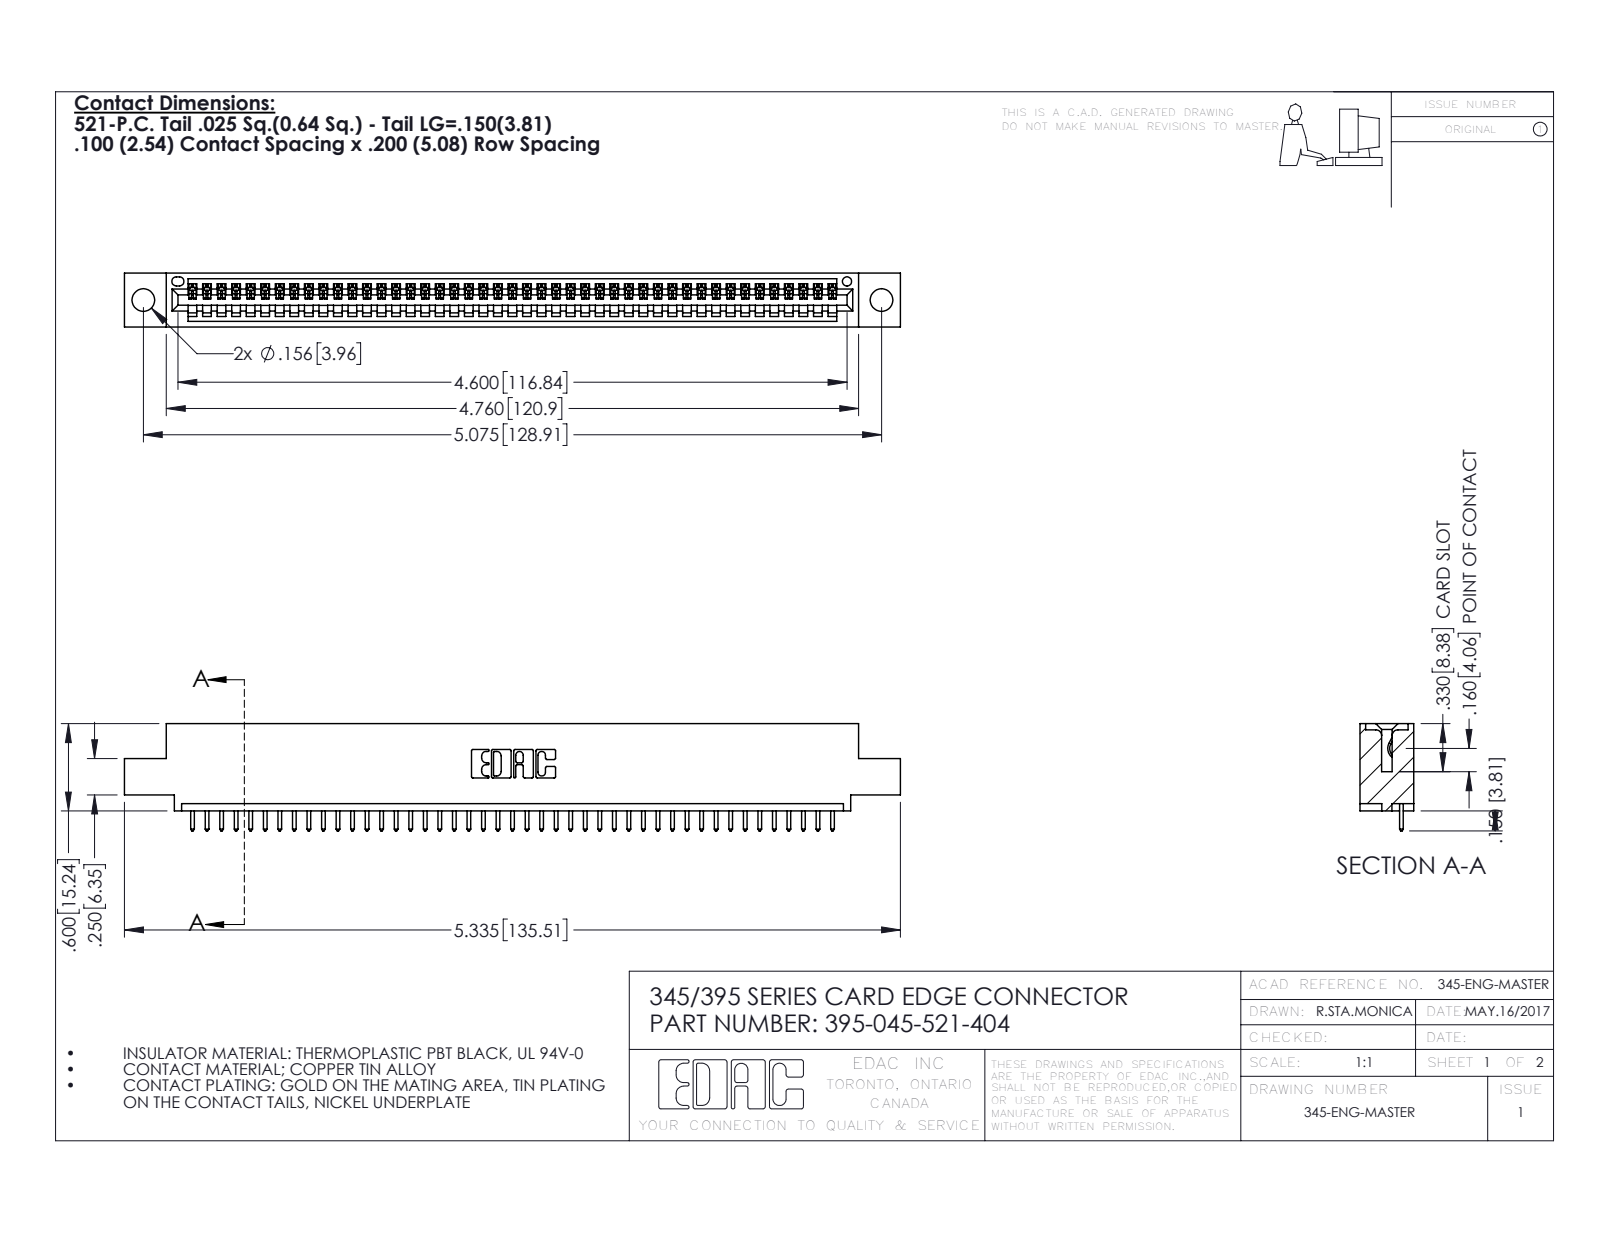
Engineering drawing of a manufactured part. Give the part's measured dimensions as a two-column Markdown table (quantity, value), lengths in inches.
| quantity | value |
| --- | --- |
| part name | 345 Part_0.110 Offset - 0.156 Dia-TH; 345-292-001_345-293-121; 395-045-521-404 |
| STEP written by | SolidWorks 2016 (CONFIG_CONTROL_DESIGN) |
| units | inches |
| bodies | 46 solids, 2740 faces (1884 planar, 856 cylindrical, 0 other) |
| overall size | 5.335 × 0.737 × 0.37 |
| volume | 0.769 in³ |
| surface area | 25.08 in² |
| round holes (diameter × count) | 0.156 × 2, 0.064 × 1 |
| partial cylindrical surfaces (radius × count) | 0.006 × 90, 0.01 × 90, 0.01 × 22, 0.007 × 6, 0.031 × 6, 0.026 × 3, 0.031 × 2, 0.04 × 2 |
| main face-to-face distances | 0.298, 0.072, 0.37, 0.2, 0.098, 0.272, 0.025, 0.225, 0.149, 0.072 |
| hole center spacings | 0.27, 4.839, 5.075 |
